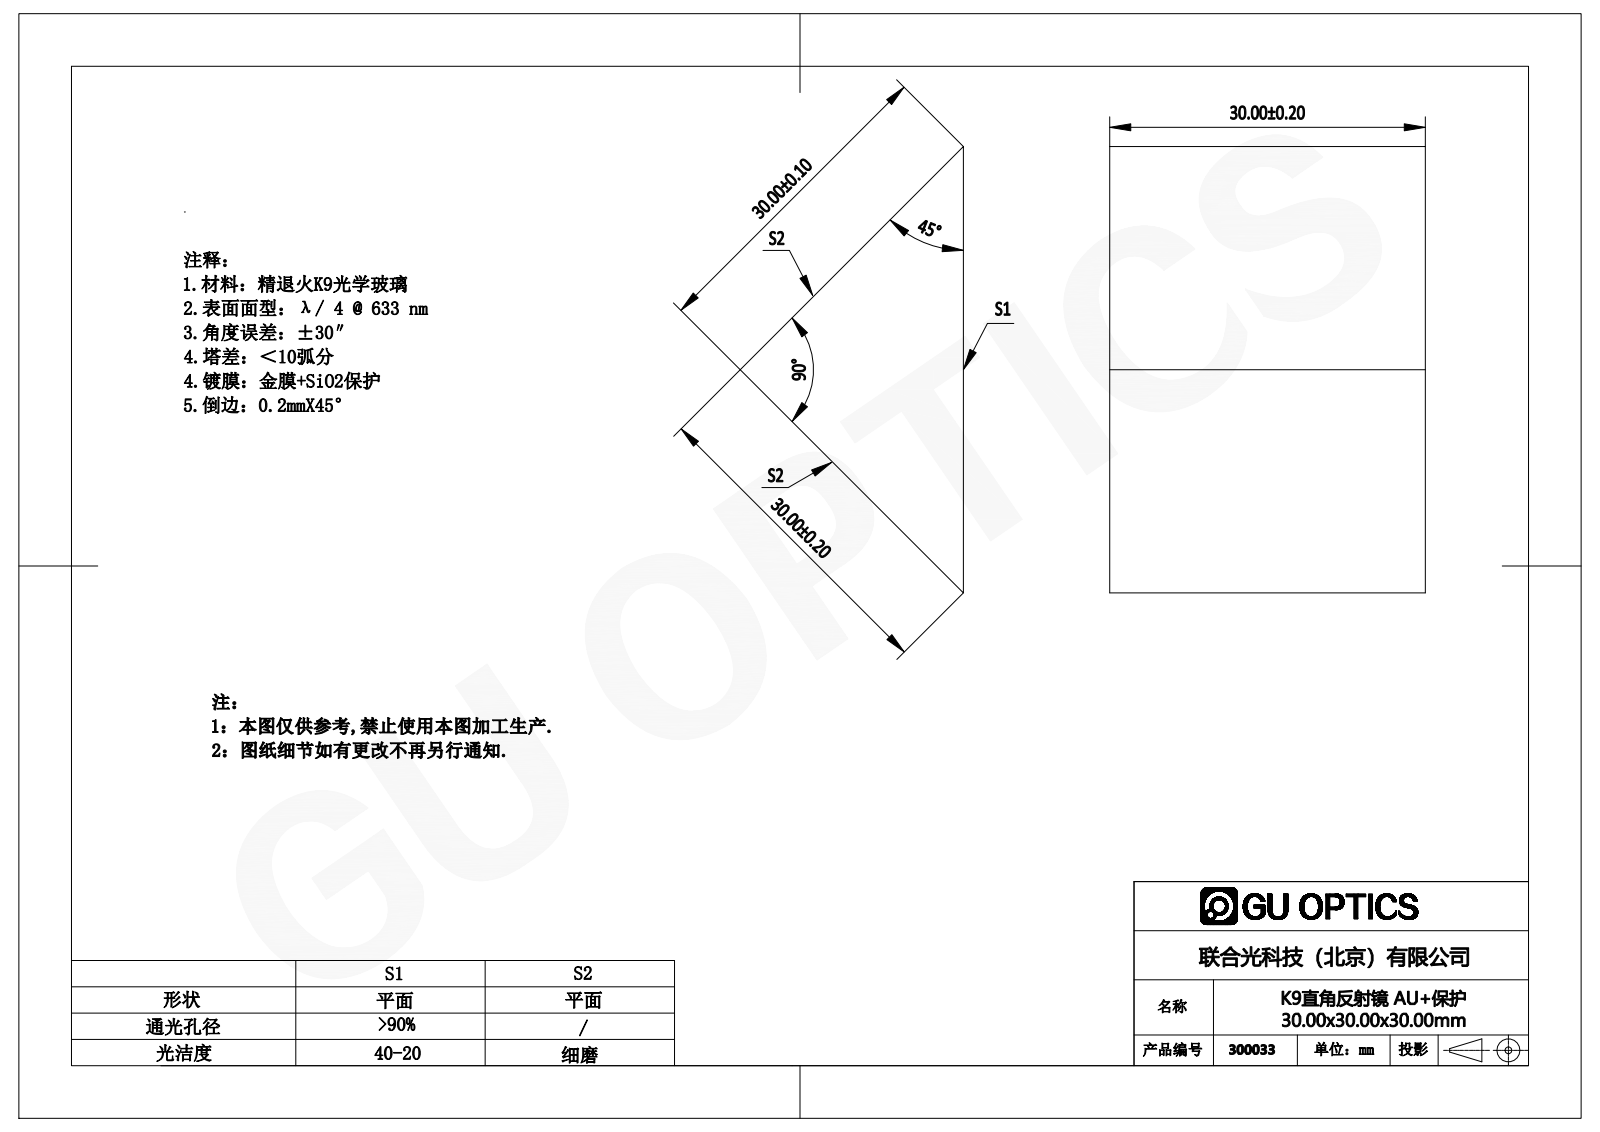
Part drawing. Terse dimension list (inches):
name: 300006
written by: SolidWorks 2016 (AUTOMOTIVE_DESIGN)
unit: in
bodies: 1 solid, 5 faces (5 planar, 0 cylindrical, 0 other)
size: 1.67 × 1.181 × 0.835
volume: 0.824 in³; area: 6.158 in²
face distances: 1.181
